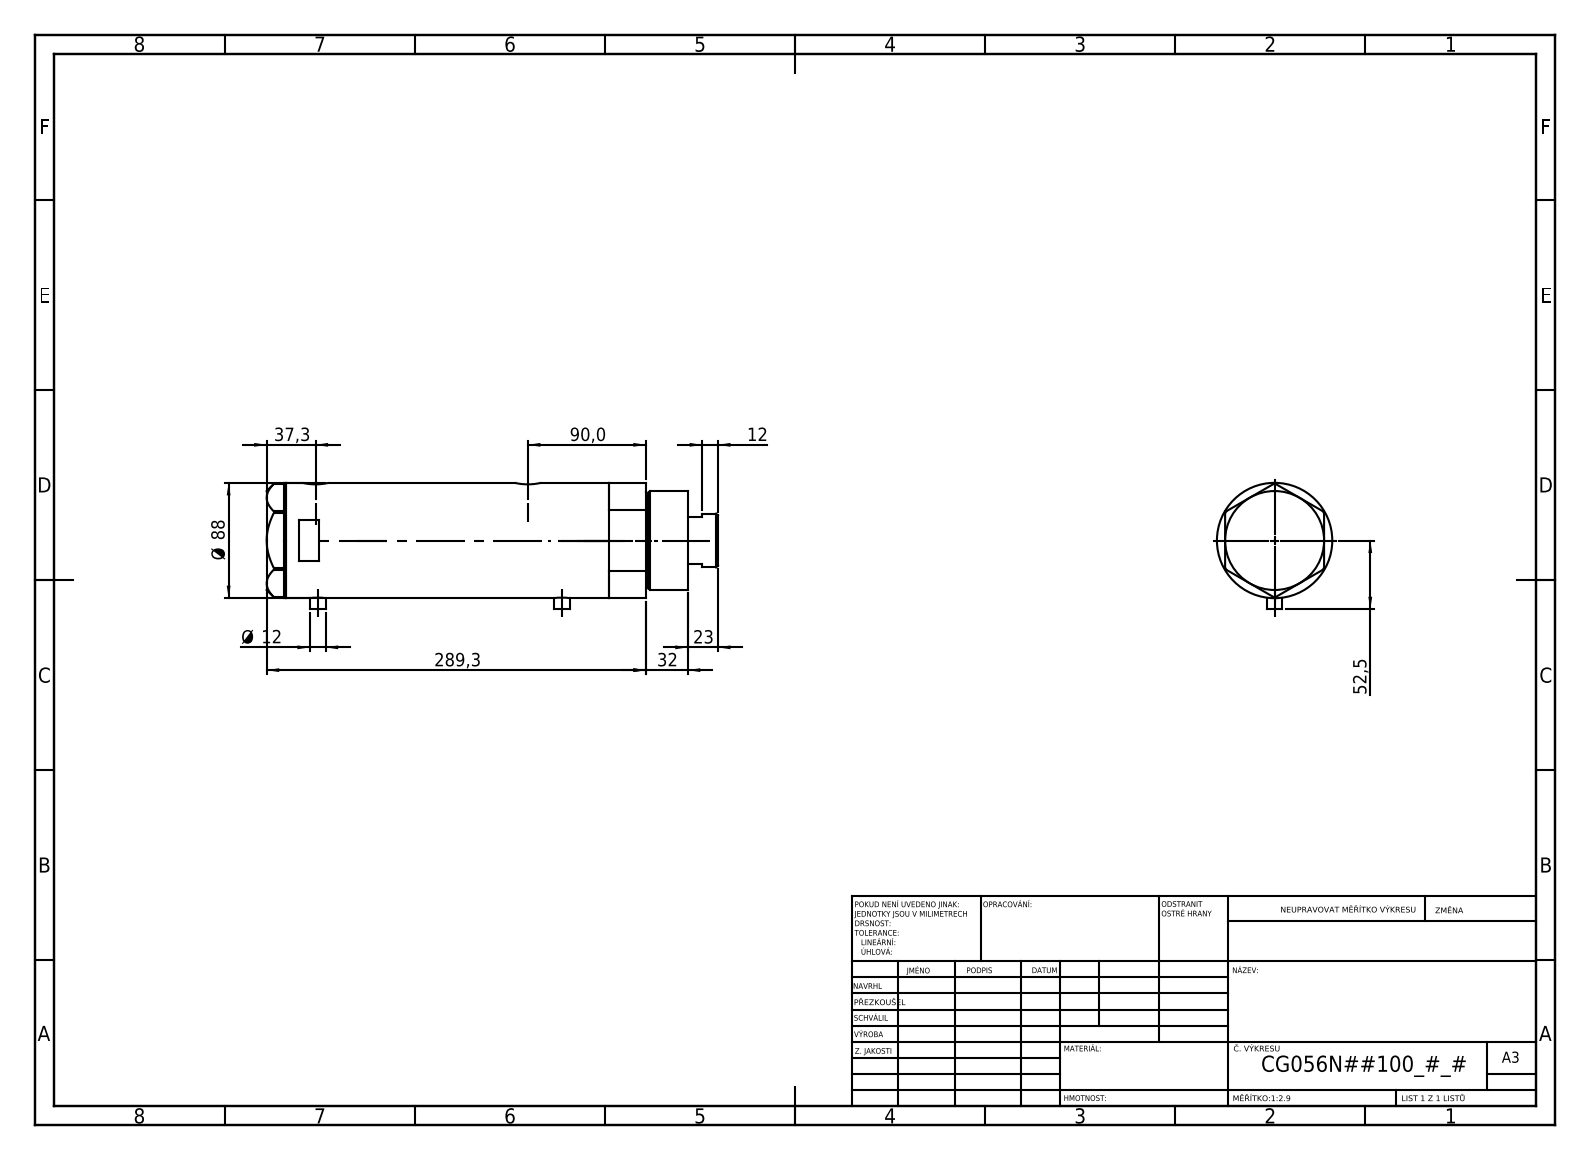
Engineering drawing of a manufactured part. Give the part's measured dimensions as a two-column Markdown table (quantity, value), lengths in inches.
| quantity | value |
| --- | --- |
| part name | V270CG_BACK; V270CG_FRONT; V270CG_MIDDLE; V270CG_VC |
| STEP written by | SolidWorks 2019 (CONFIG_CONTROL_DESIGN) |
| units | inches |
| bodies | 4 solids, 121 faces (52 planar, 49 cylindrical, 20 other) |
| overall size | 13.555 × 3.799 × 3.465 |
| volume | 108.9 in³ |
| surface area | 388.5 in² |
| round holes (diameter × count) | 0.492 × 2, 0.518 × 2, 0.787 × 2, 0.571 × 1, 1.654 × 1, 1.713 × 1, 2.205 × 1, 2.362 × 1, 3.15 × 1 |
| round bosses / shafts (diameter × count) | 0.472 × 2, 3.465 × 1, 2.953 × 1, 2.874 × 1, 1.614 × 1 |
| main face-to-face distances | 7.26, 1.024, 6.236, 0.591, 1.614, 7.85, 12.059, 12.65, 11.035, 4.799 |
| hole center spacings | 0.067, 1.016, 6.311, 6.378, 7.327, 7.394 |
